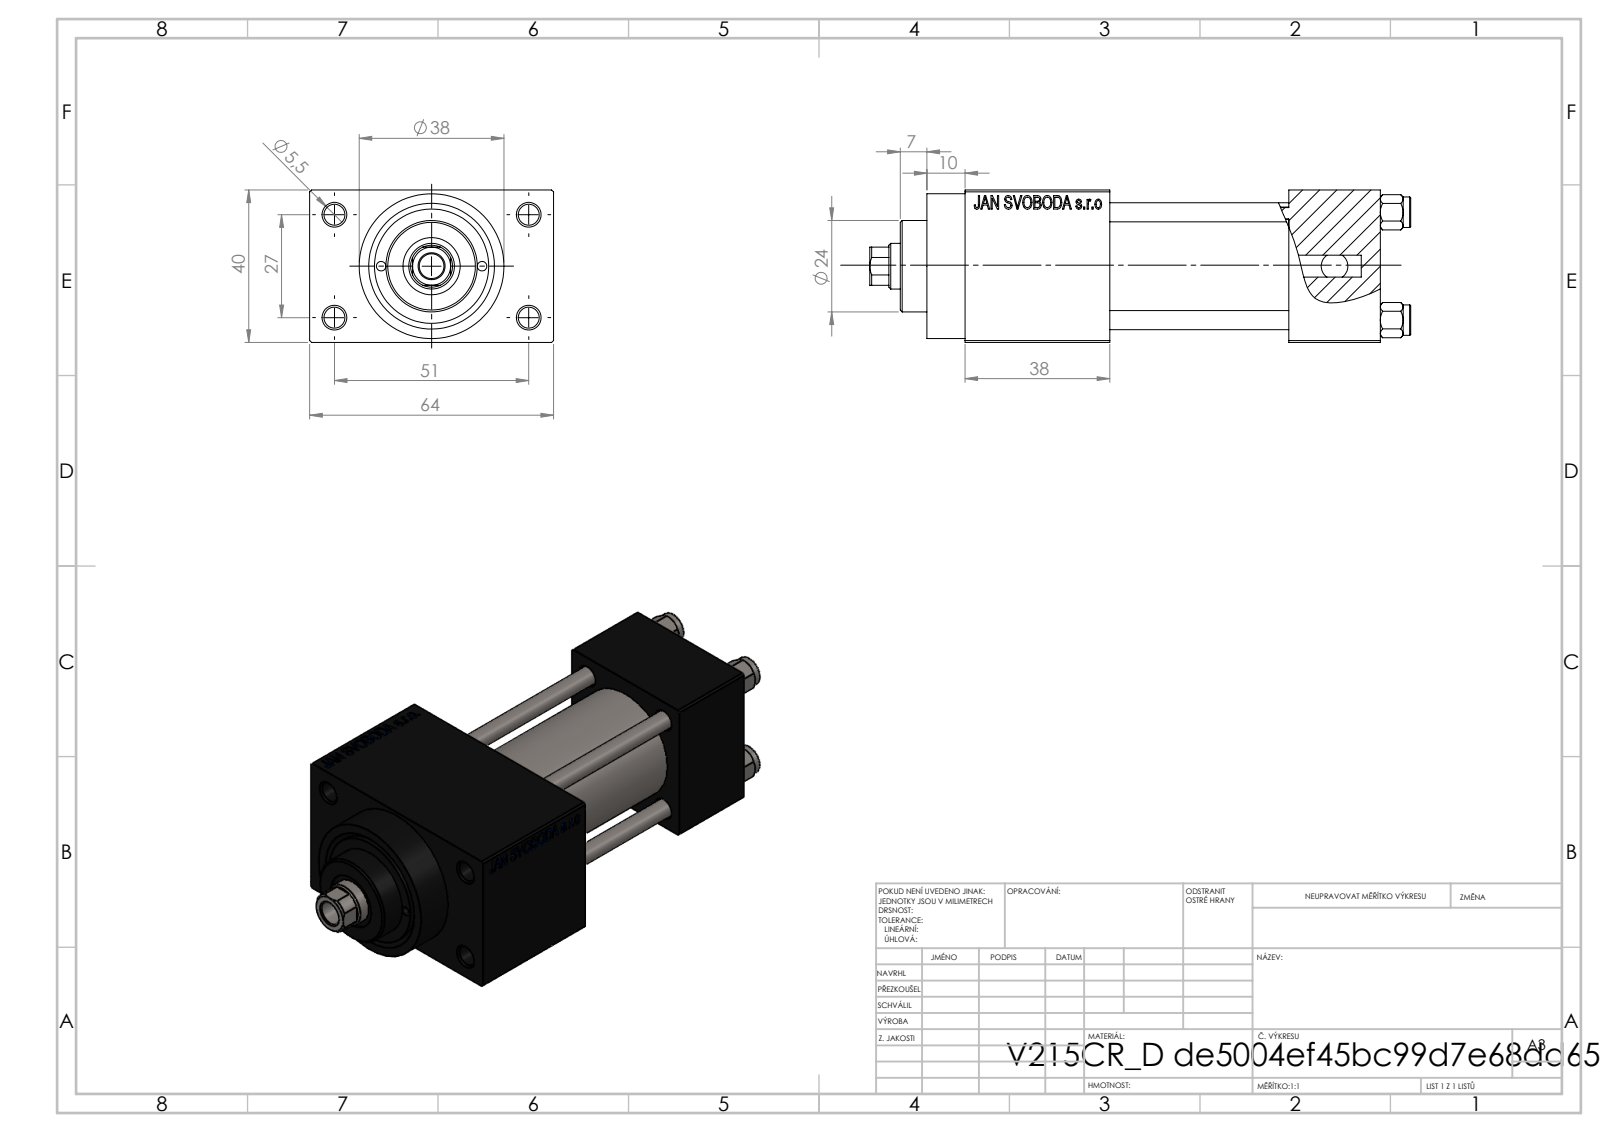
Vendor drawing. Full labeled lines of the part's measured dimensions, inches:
Part name (STEP PRODUCT): V215CR_D_Body; V215_VC_A; NUT_M5_D; V215CR_D_TYCINKA (+1 more)
STEP written by: SolidWorks 2019 (CONFIG_CONTROL_DESIGN)
Units: inches
Bodies: 11 solids, 1110 faces (498 planar, 92 cylindrical, 520 other)
Overall size (bounding box): 5.591 × 2.52 × 1.575
Volume: 10.59 in³ · Surface area: 96.35 in²
Round holes (diameter × count): ⌀0.197 ×4, ⌀0.217 ×4, ⌀0.787 ×3, ⌀0.098 ×2, ⌀0.276 ×2, ⌀0.518 ×2, ⌀0.256 ×1, ⌀0.472 ×1, ⌀0.591 ×1, ⌀0.984 ×1, ⌀1.181 ×1
Round bosses / shafts (diameter × count): ⌀0.315 ×4, ⌀1.496 ×1, ⌀1.22 ×1, ⌀0.945 ×1
Partial cylindrical surfaces — rounded edges, fillets, slot ends (radius × count): R0.217 ×1
Main face-to-face distances: 1.575, 0.472, 1.85, 0.945, 2.795, 2.047, 1.496, 4.291, 3.346, 2.52
Hole centre spacings: 0.448, 0.558, 0.718, 0.788, 1.114, 1.136, 1.177, 1.214
